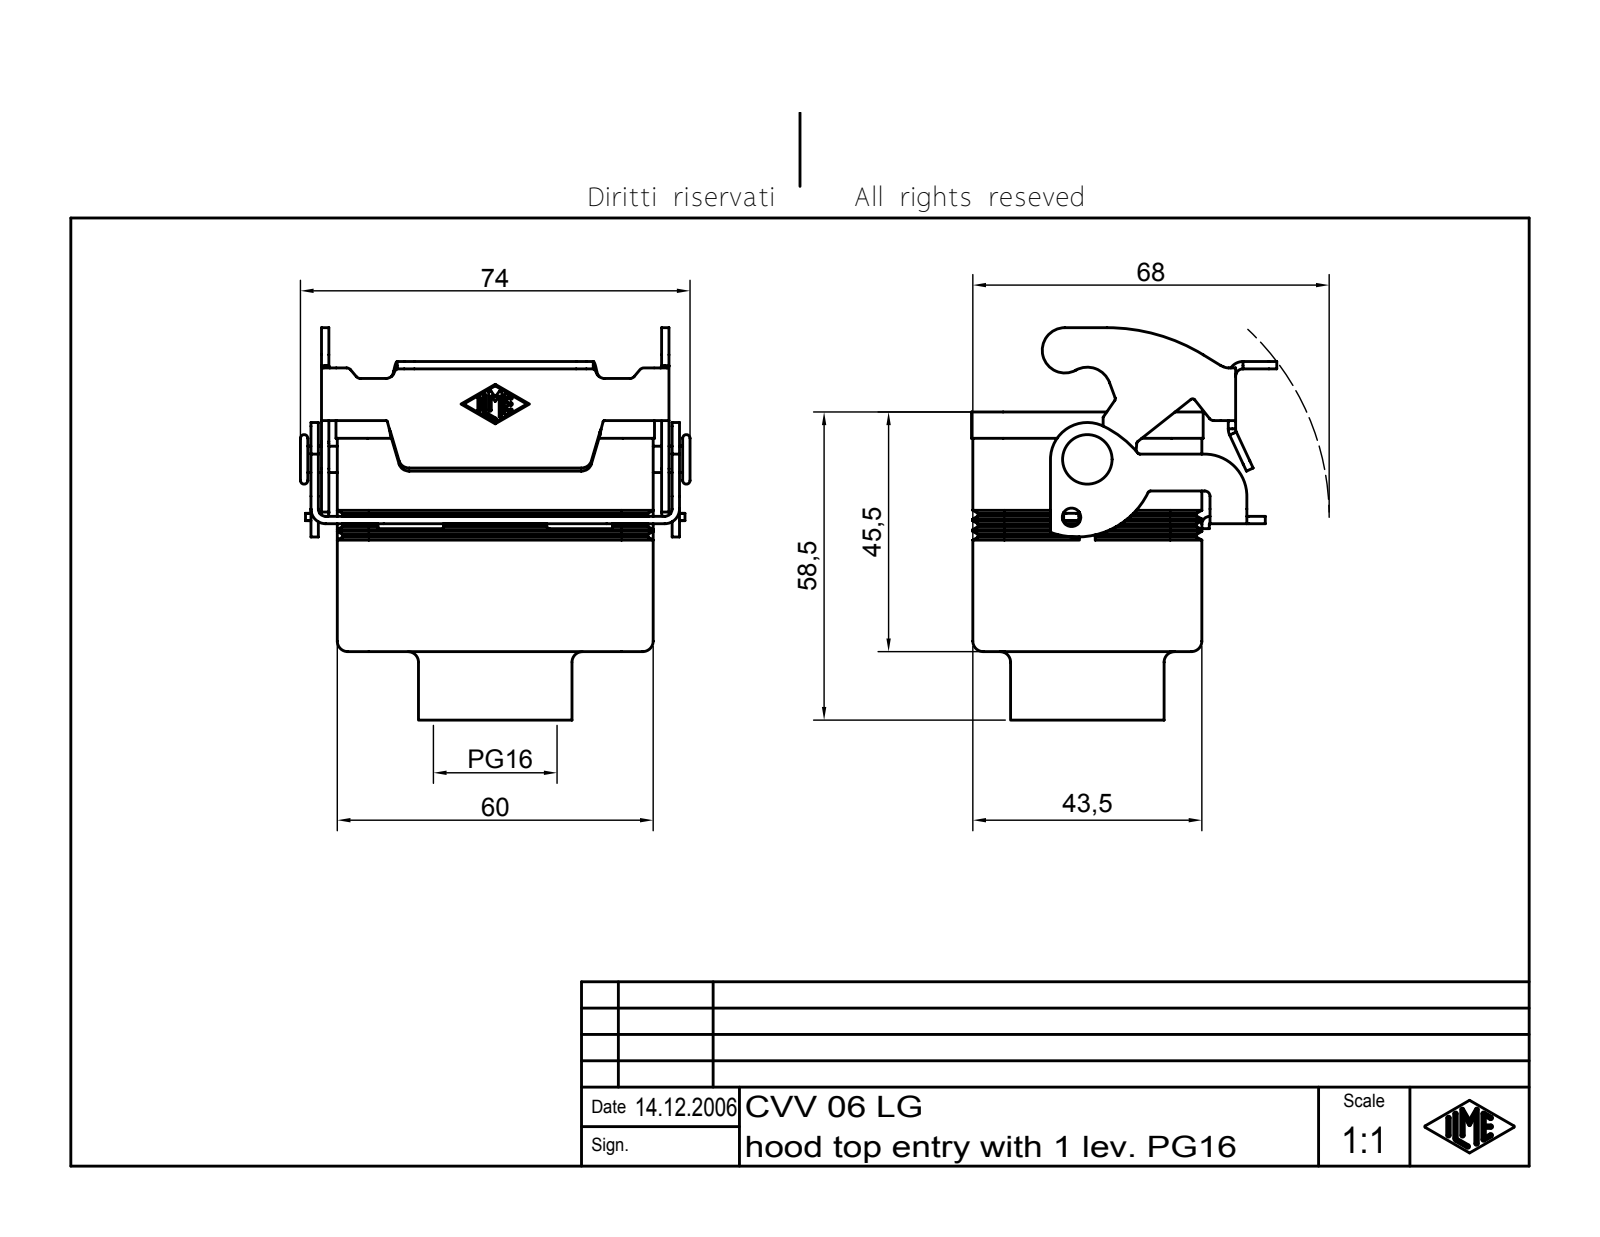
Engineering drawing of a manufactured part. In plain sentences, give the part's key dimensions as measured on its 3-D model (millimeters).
The part is named "CVV 06 LG". Its 3-D file was written by "Autodesk Inventor 7 (AUTOMOTIVE_DESIGN)". It is 2 solids with 494 faces: 155 planar, 127 cylindrical and 212 other. Overall it measures 74.5 by 74 by 57.98 millimeters. Its volume is 49 662 cubic millimeters and its surface area 34 251 square millimeters. Round holes: 1 of diameter 3.5, 1 of diameter 18.16, 1 of diameter 21.16. Round bosses or shafts: 1 of diameter 29.16, 1 of diameter 5, 1 of diameter 3.2. Partial cylindrical surfaces (rounded edges, fillets, slot ends): 15 of radius 0.25, 10 of radius 2, 9 of radius 0.5, 9 of radius 1.5, 8 of radius 1, 8 of radius 6, 6 of radius 1.4, 6 of radius 2.8. The main face-to-face distances are 3, 40.5, 37.5, 57, 1.4, 45.5, 43.5, 60, 11.75, 2.
